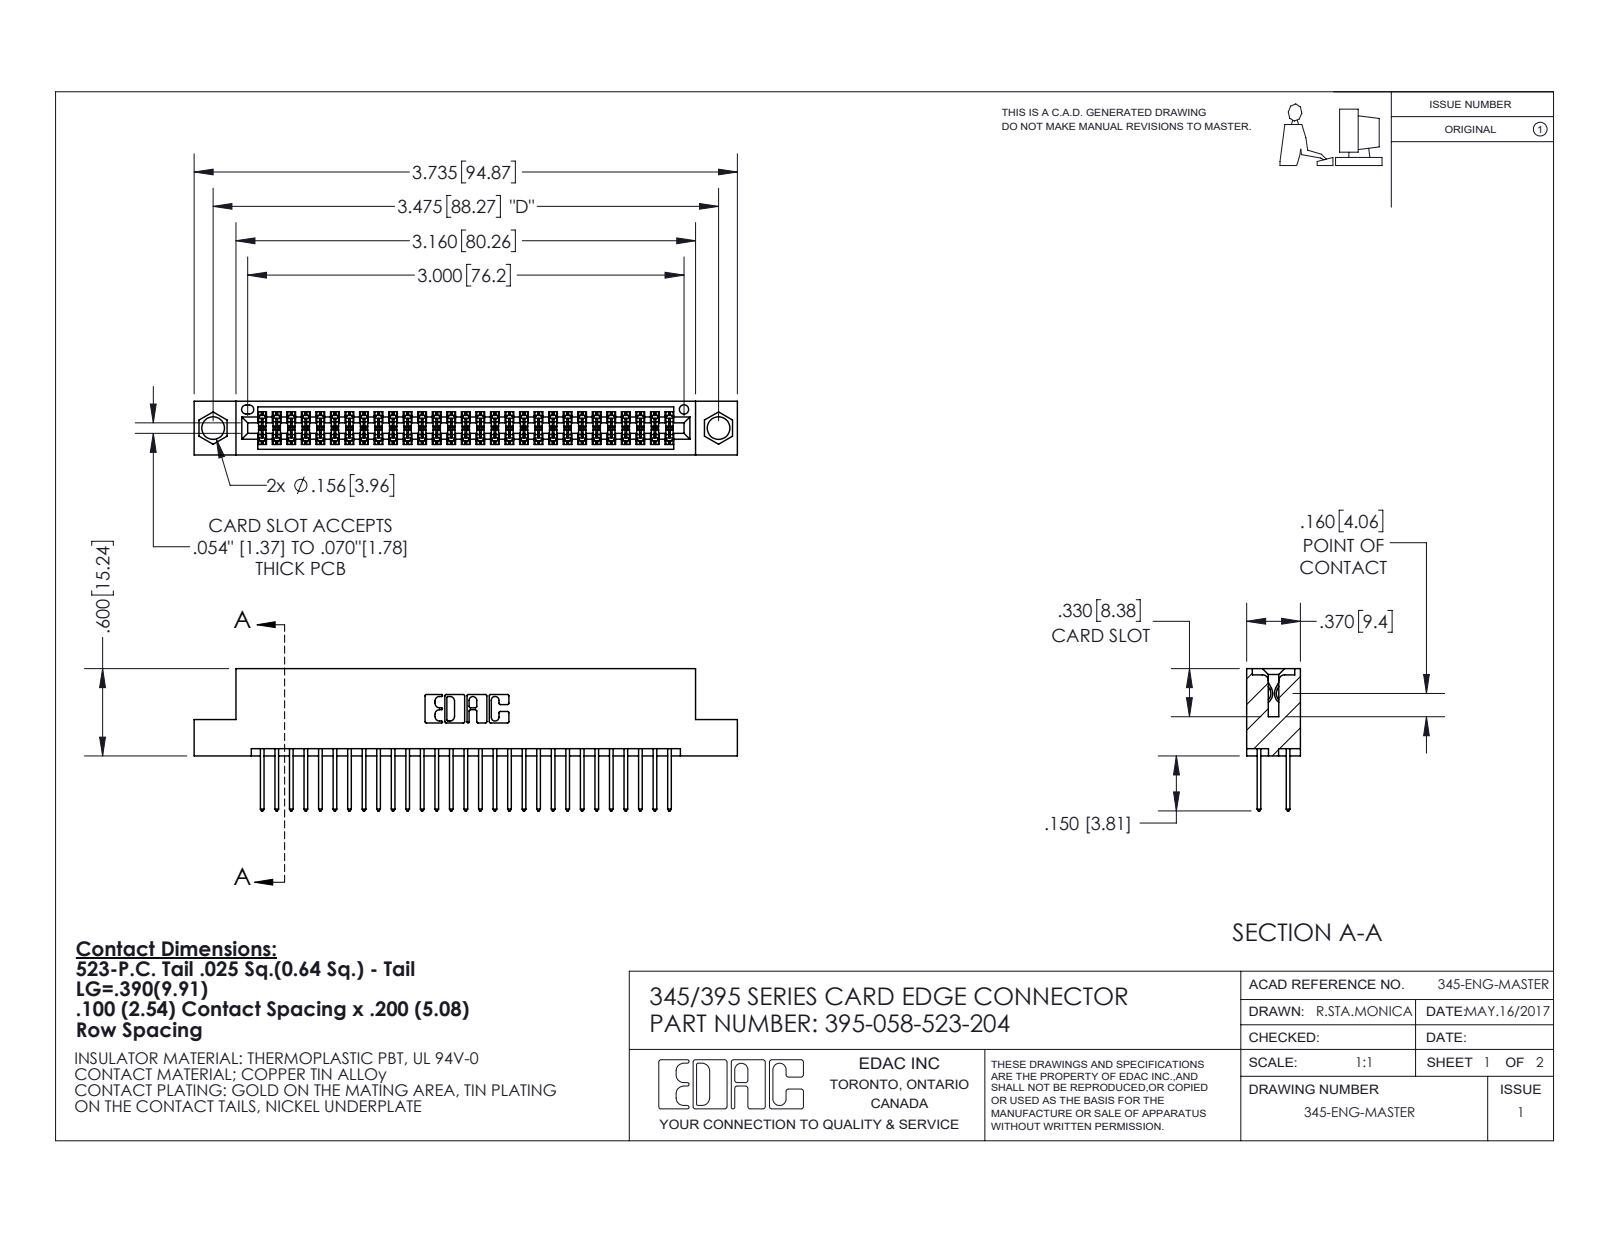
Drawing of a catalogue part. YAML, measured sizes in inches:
part_name: "395-058-523-204; 345 Part_Flush Mounting Lugs - 0.156 Dia-TI; 345-292-001_345-293-123"
step_written_by: "SolidWorks 2020 (CONFIG_CONTROL_DESIGN)"
units: inches
bodies: {solids: 59, faces: 3040, planar: 2008, cylindrical: 1032, other: 0}
overall_size: [3.735, 0.977, 0.37]
volume: 0.556
surface_area: 21.07
round_holes:
  - {diameter: 0.156, count: 2}
  - {diameter: 0.064, count: 1}
partial_cylinders:
  - {radius: 0.006, count: 116}
  - {radius: 0.01, count: 58}
  - {radius: 0.01, count: 22}
  - {radius: 0.007, count: 6}
  - {radius: 0.031, count: 6}
  - {radius: 0.026, count: 3}
  - {radius: 0.014, count: 2}
  - {radius: 0.019, count: 2}
face_to_face_distances: [0.072, 0.298, 0.2, 0.098, 0.272, 0.025, 0.37, 0.225, 0.175, 0.149]
hole_center_spacings: [0.27, 3.24, 3.475]
